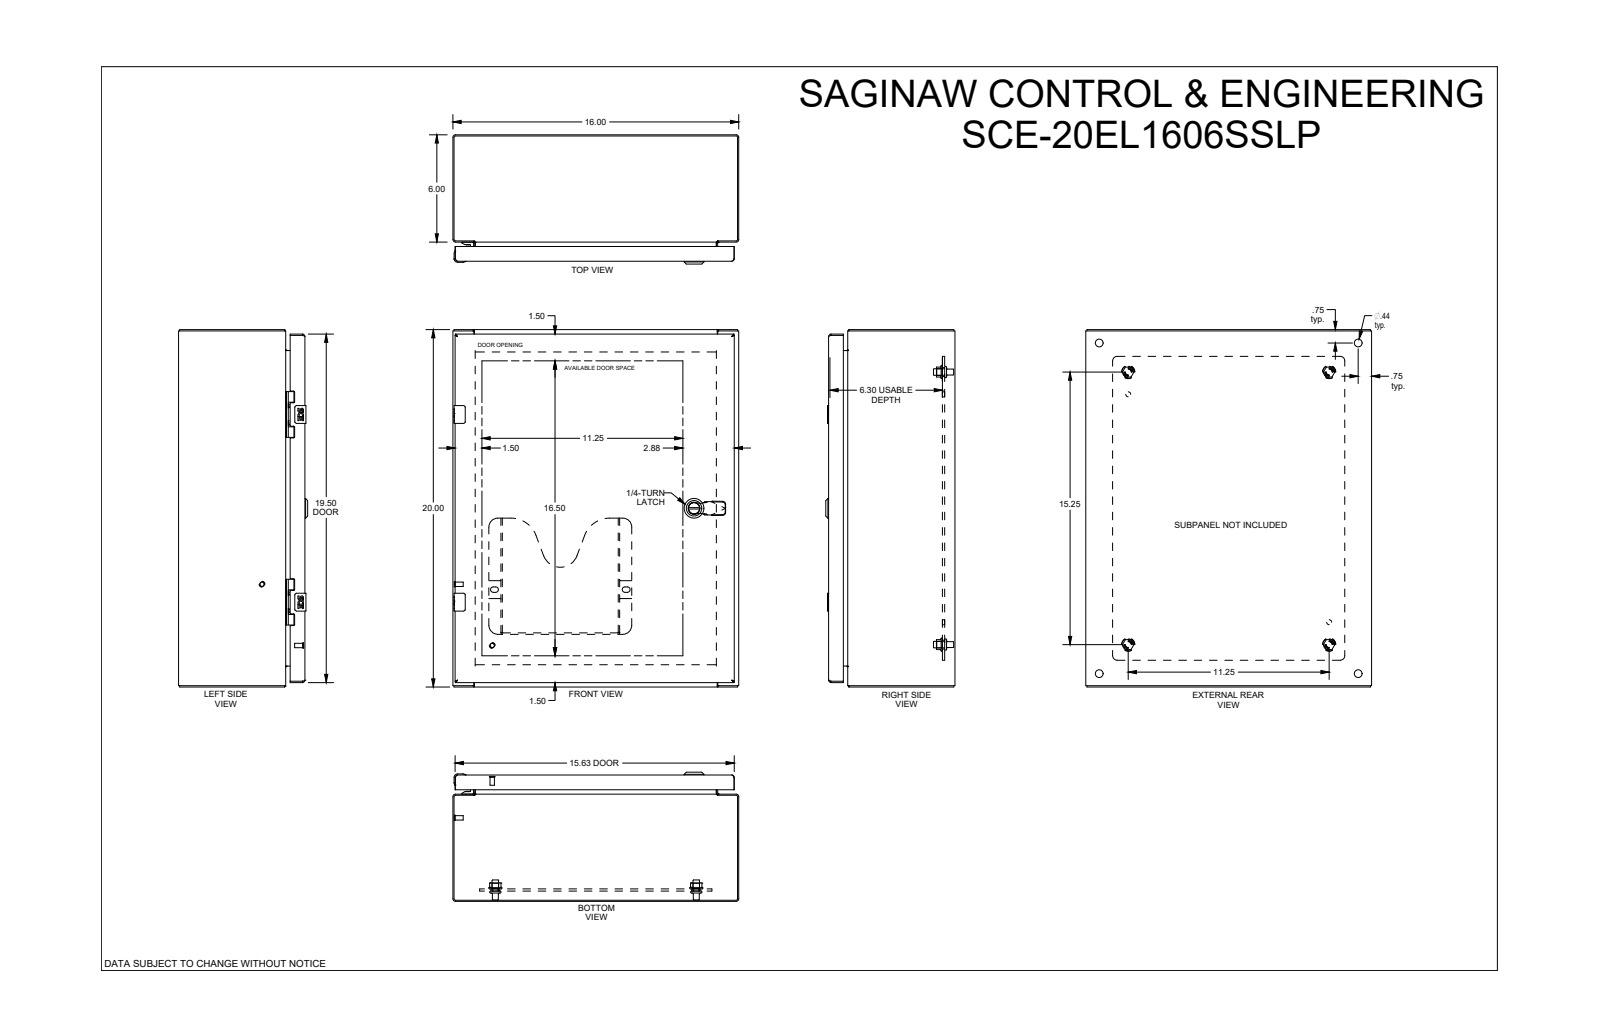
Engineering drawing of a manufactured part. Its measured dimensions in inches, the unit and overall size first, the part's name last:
Units: inches
Overall size (bounding box): 20 × 16 × 7.936
Round holes (diameter × count): ⌀0.172 ×4, ⌀0.205 ×4, ⌀0.244 ×4, ⌀0.375 ×4, ⌀0.437 ×4, ⌀0.5 ×4, ⌀0.04 ×2, ⌀0.188 ×2, ⌀0.218 ×2, ⌀0.281 ×2, ⌀0.197 ×1, ⌀0.204 ×1
Round bosses / shafts (diameter × count): ⌀0.375 ×4, ⌀0.33 ×4, ⌀0.25 ×4, ⌀0.248 ×4, ⌀0.24 ×4, ⌀1.102 ×1, ⌀0.78 ×1, ⌀0.63 ×1
Partial cylindrical surfaces — rounded edges, fillets, slot ends (radius × count): R0.015 ×24, R0.04 ×17, R0.22 ×16, R0.043 ×12, R0.118 ×12, R0.031 ×10, R0.06 ×9, R0.062 ×8
Main face-to-face distances: 0.075, 0.06, 6.993, 7.068, 7.008, 6.933, 15.925, 0.125, 0.5, 0.575
Hole centre spacings: 0.494, 10.5, 0.984, 1.25, 2.317, 2.319, 2.452, 2.87
Volume: 133.2 in³ · Surface area: 3 217 in²
Bodies: 24 solids, 1217 faces (544 planar, 474 cylindrical, 199 other)
Part name (STEP PRODUCT): SCE-20EL1606LP_rev1
STEP written by: SolidWorks 2021 (AUTOMOTIVE_DESIGN)
